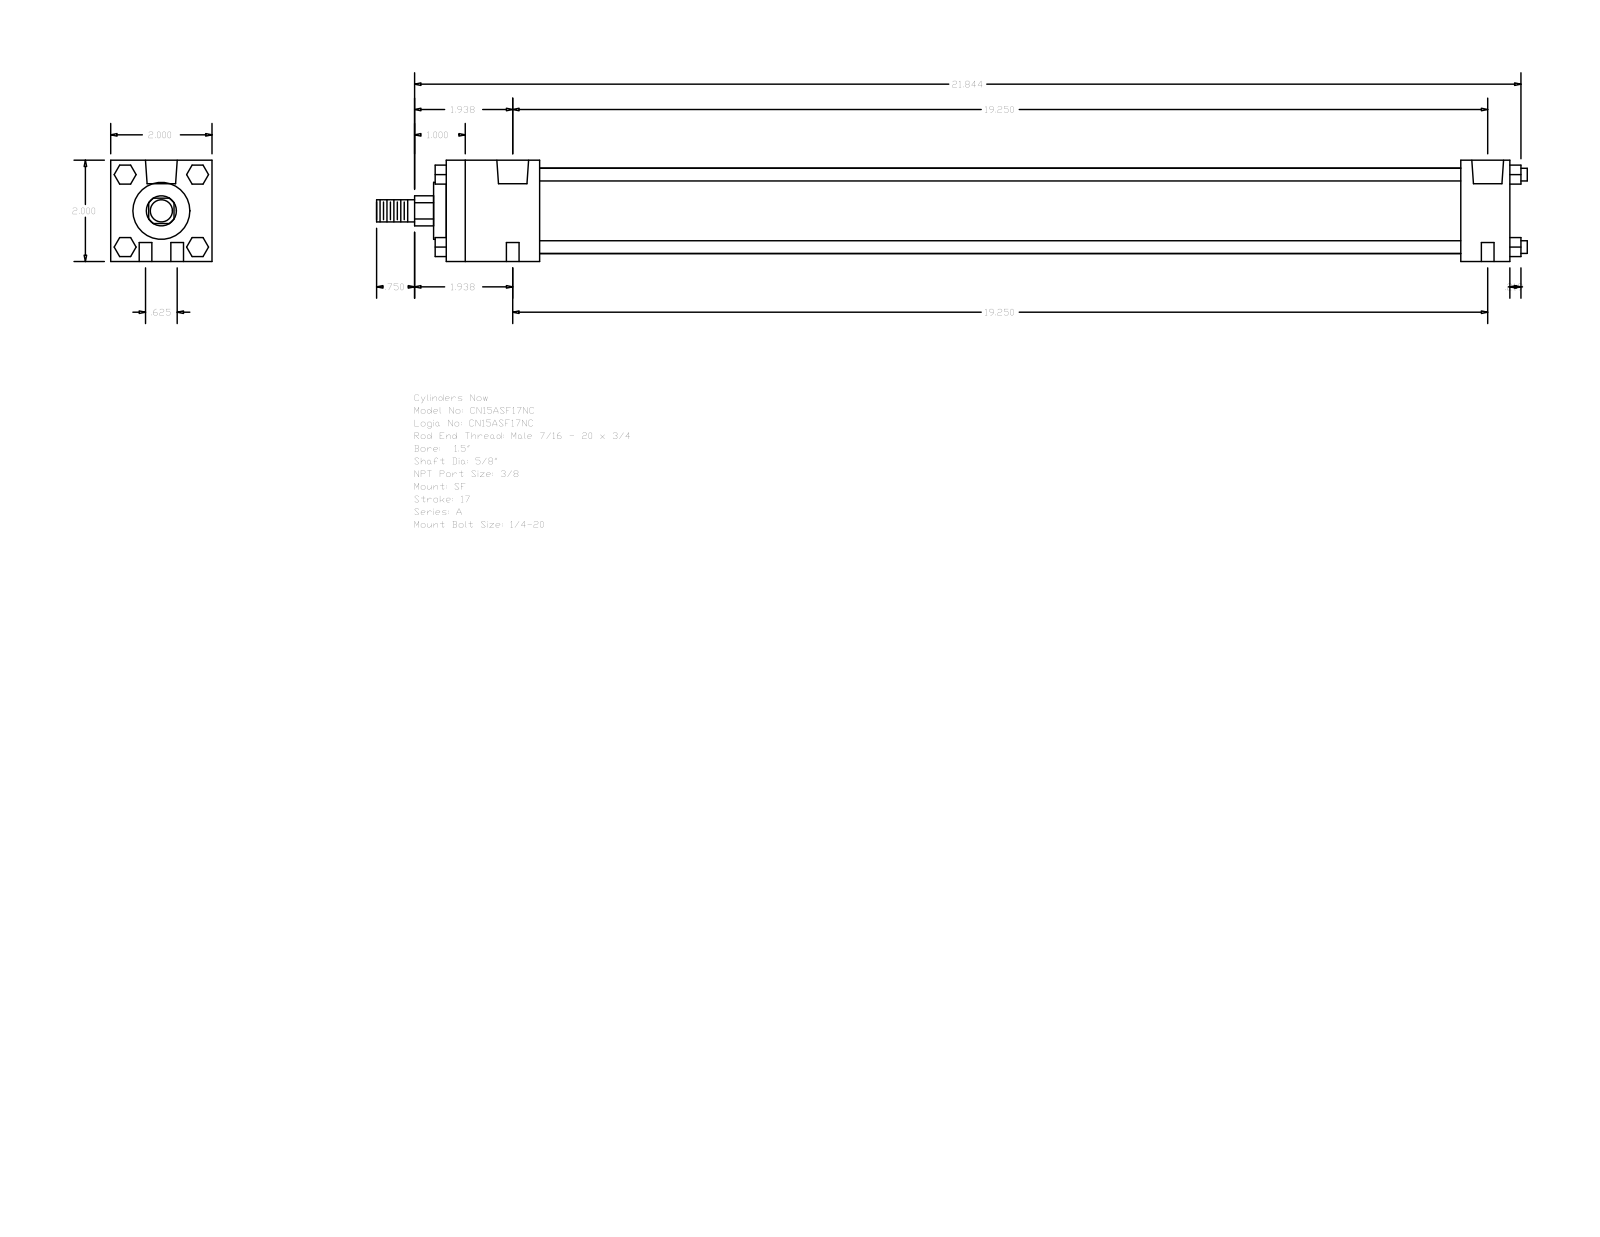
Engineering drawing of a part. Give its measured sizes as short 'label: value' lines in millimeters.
name: A_SF__0150_0.625
written by: GSSL Pune (CONFIG_CONTROL_DESIGN)
unit: mm
bodies: 0 solids, 124 faces (94 planar, 30 cylindrical, 0 other)
size: 577.06 × 50.8 × 50.8
holes: 4× ⌀6.35, 2× ⌀5.56, 2× ⌀15.93
bosses: 4× ⌀6.35, 1× ⌀42.93, 1× ⌀28.57, 1× ⌀15.88, 1× ⌀11.11
rounds: 1× R7.54
face distances: 50.8, 533.39, 46.83, 508.79, 461.96, 486.56, 24.6, 6.35, 9.52, 53.18
hole spacings: 7.94, 489.01, 488.95, 15.88, 489.21, 481.01
